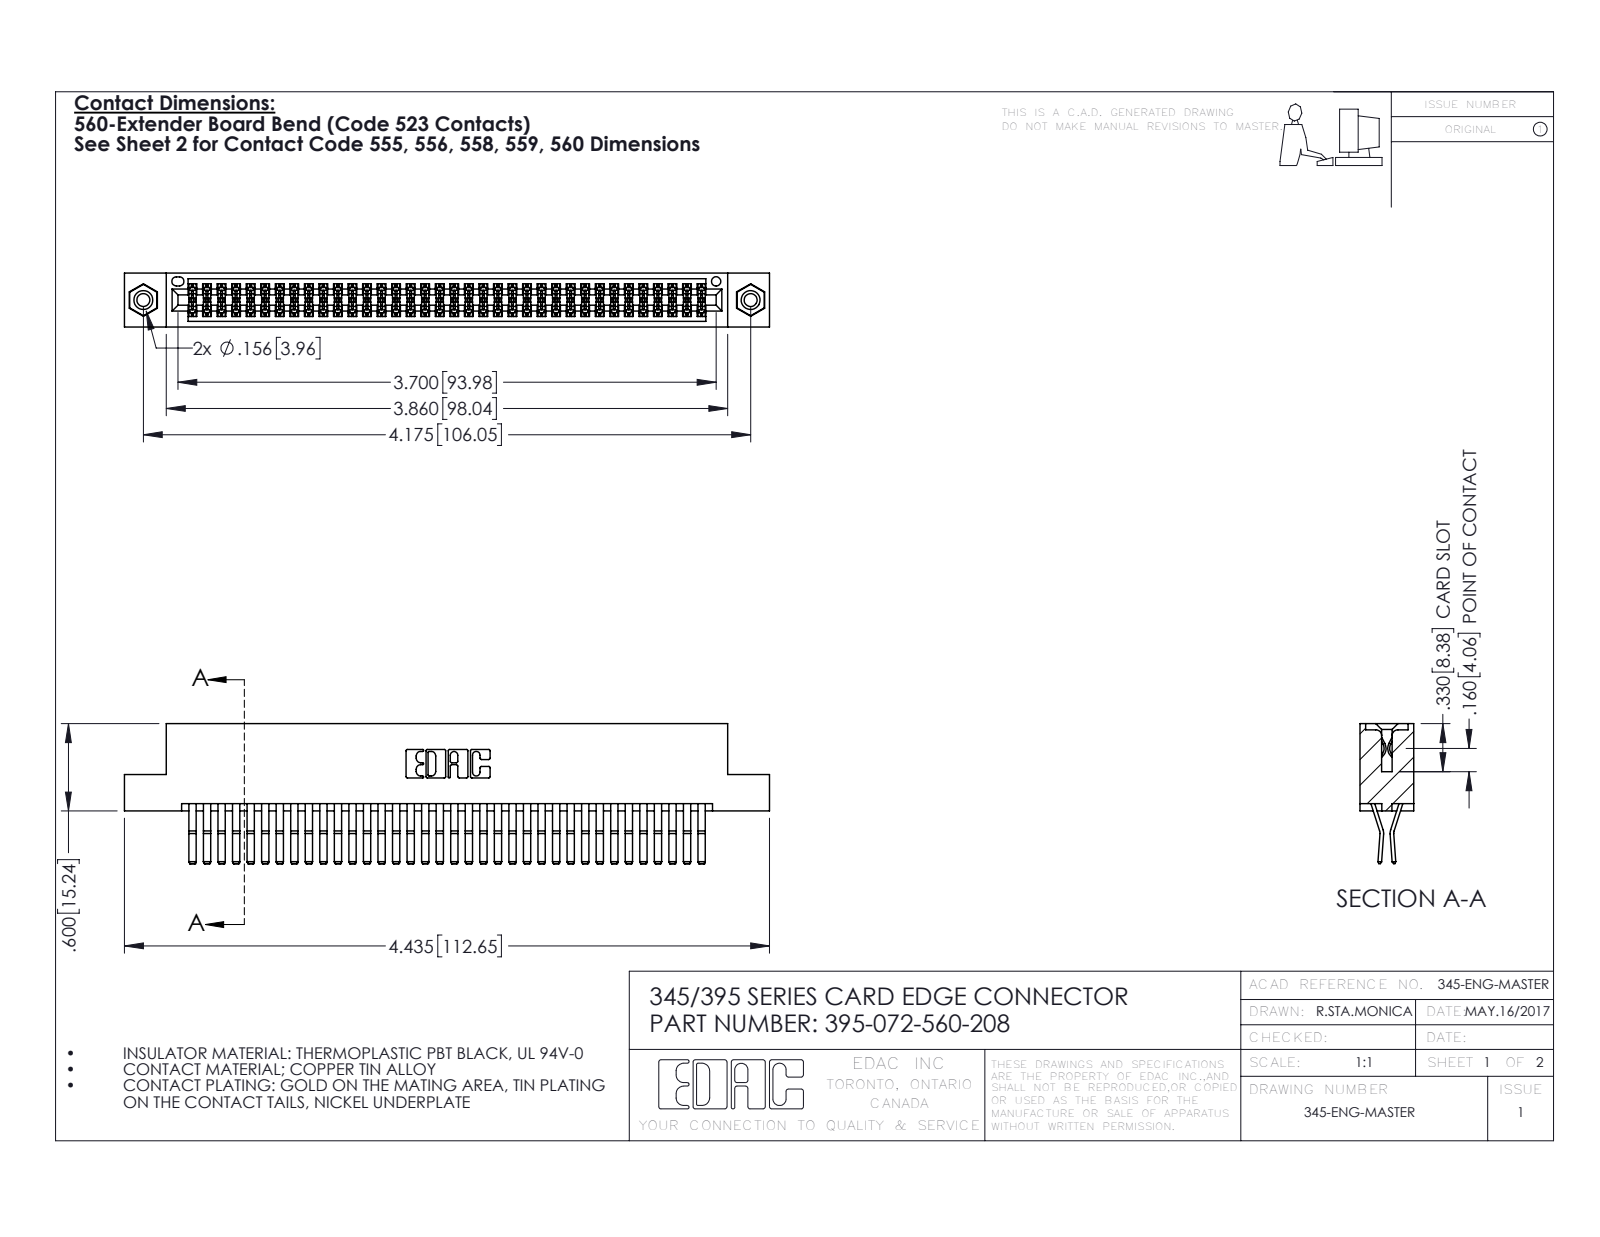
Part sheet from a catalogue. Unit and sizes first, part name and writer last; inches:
Units: inches
Overall size (bounding box): 4.435 × 0.962 × 0.37
Round holes (diameter × count): ⌀0.089 ×2, ⌀0.125 ×2, ⌀0.156 ×2, ⌀0.064 ×1
Round bosses / shafts (diameter × count): ⌀0.155 ×2
Partial cylindrical surfaces — rounded edges, fillets, slot ends (radius × count): R0.006 ×108, R0.01 ×22, R0.007 ×6, R0.031 ×6, R0.026 ×3, R0.01 ×2, R0.014 ×2, R0.019 ×2
Main face-to-face distances: 0.025, 0.072, 0.298, 0.37, 0.2, 0.098, 0.272, 0.225, 0.175, 0.149
Hole centre spacings: 0.27, 3.939, 4.175
Volume: 0.693 in³ · Surface area: 27.73 in²
Bodies: 75 solids, 3930 faces (2488 planar, 1426 cylindrical, 16 other)
Part name (STEP PRODUCT): 345-292-001_560 Tail; 345 Part_Flush Mounting Lugs - 0.156 Dia-TI; 345-250-001_345-250-003-102; 395-072-560-208
STEP written by: SolidWorks 2016 (CONFIG_CONTROL_DESIGN)
